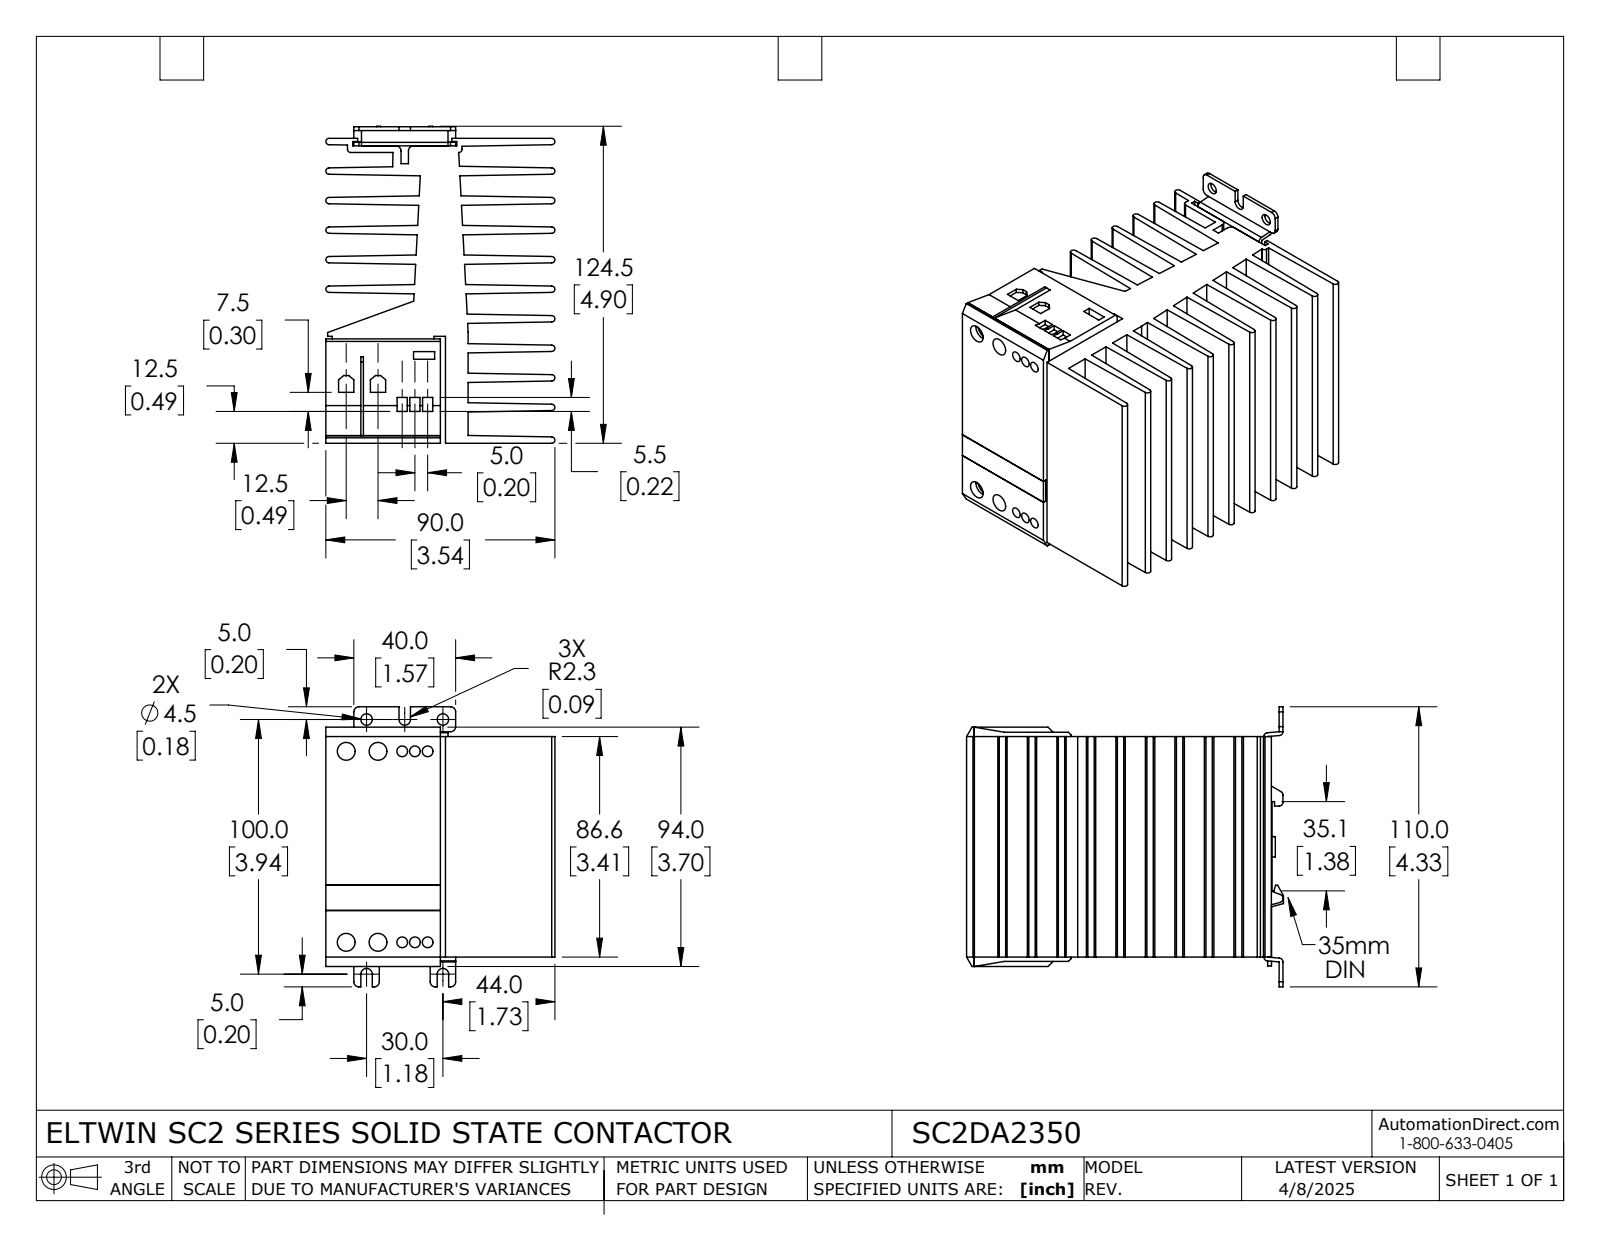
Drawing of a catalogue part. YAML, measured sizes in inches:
part_name: "SC2DA2350"
step_written_by: "SolidWorks 2021 (AUTOMOTIVE_DESIGN)"
units: inches
bodies: {solids: 7, faces: 404, planar: 294, cylindrical: 110, other: 0}
overall_size: [4.902, 4.331, 3.543]
volume: 31.2
surface_area: 277.4
round_holes:
  - {diameter: 0.165, count: 6}
  - {diameter: 0.173, count: 6}
  - {diameter: 0.276, count: 4}
  - {diameter: 0.177, count: 2}
  - {diameter: 0.315, count: 2}
round_bosses_or_shafts:
  - {diameter: 0.315, count: 3}
partial_cylinders:
  - {radius: 0.049, count: 19}
  - {radius: 0.079, count: 18}
  - {radius: 0.059, count: 10}
  - {radius: 0.051, count: 4}
  - {radius: 0.089, count: 3}
face_to_face_distances: [0.457, 0.913, 1.37, 0.159, 0.3, 0.157, 1.827, 1.669, 1.828, 2.126]
hole_center_spacings: [2.953, 0.197, 2.959, 0.374, 0.394, 0.492, 0.571, 0.768]
